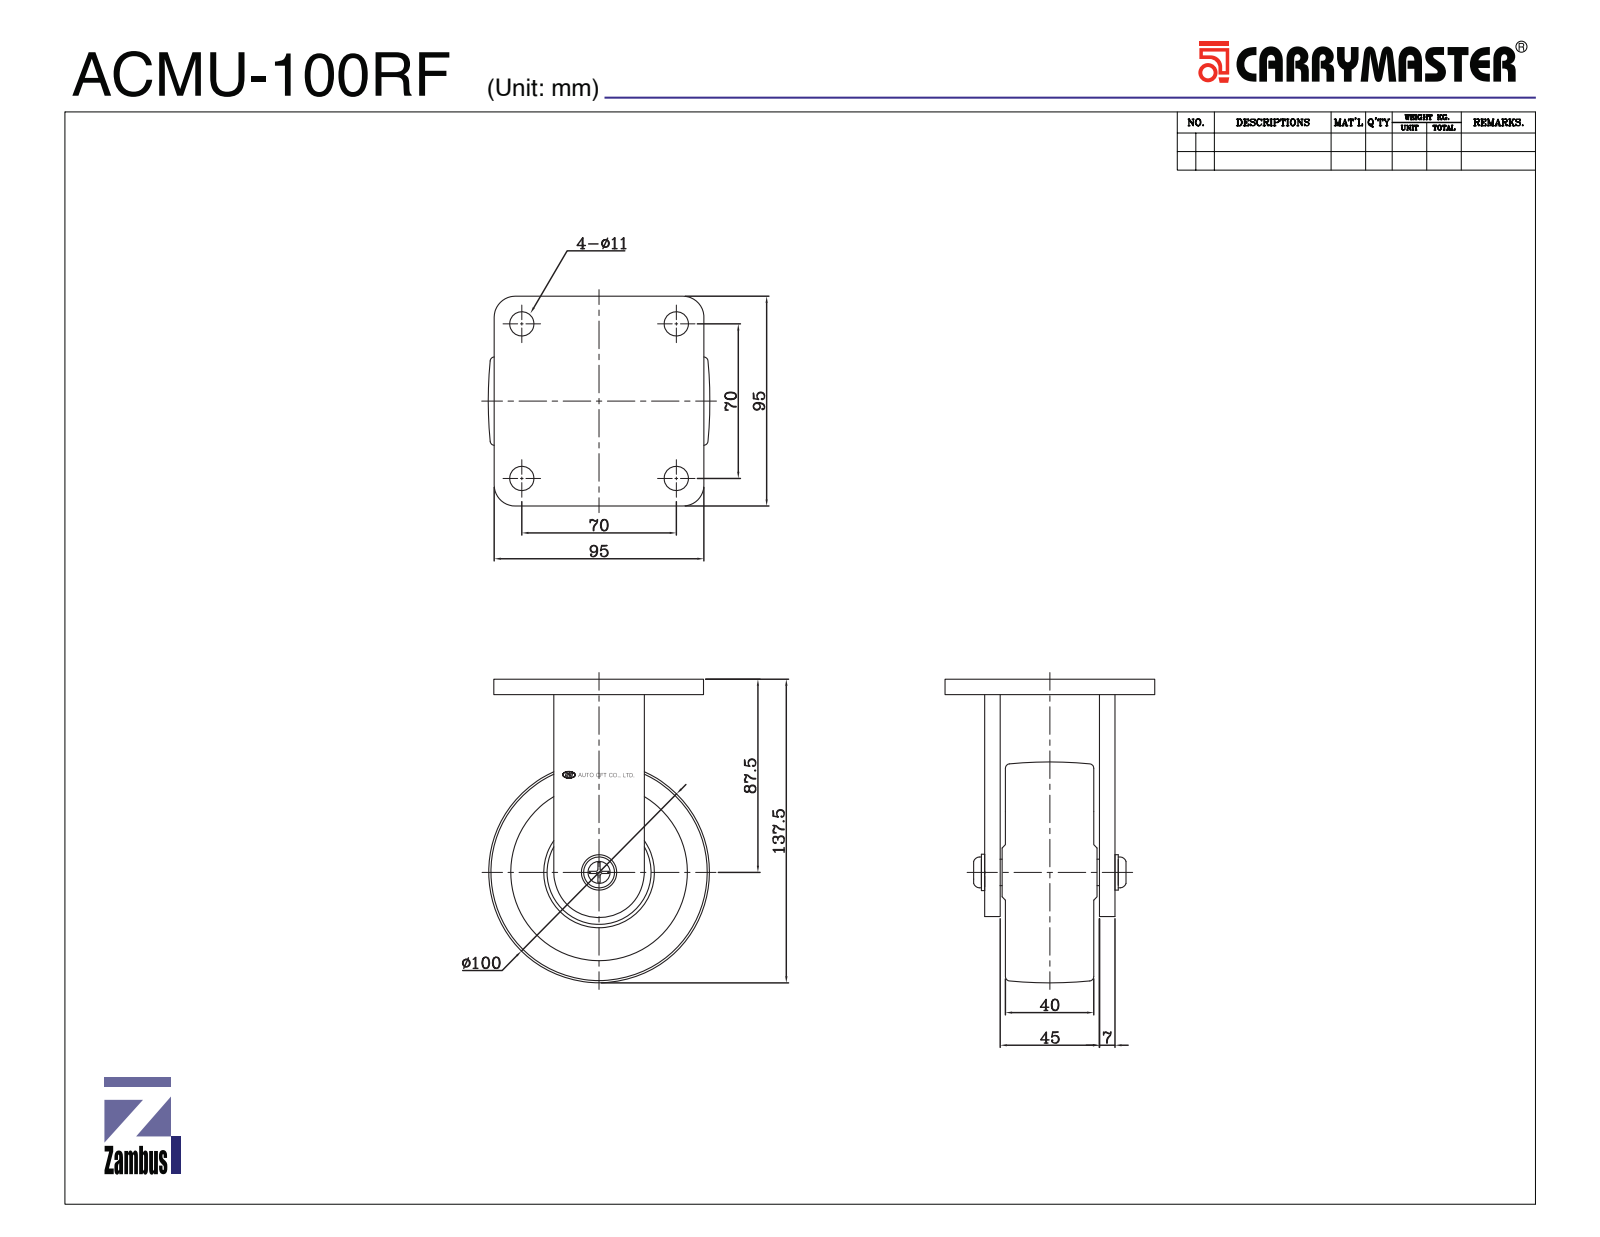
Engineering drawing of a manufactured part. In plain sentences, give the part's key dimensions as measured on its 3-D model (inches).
The part is named "ACMU-100RF". Its 3-D file was written by "SolidWorks 2015 (CONFIG_CONTROL_DESIGN)". It is 7 solids with 987 faces: 246 planar, 97 cylindrical and 644 other. Overall it measures 5.413 by 3.937 by 3.74 inches. Its volume is 22.74 cubic inches and its surface area 166.7 square inches. Round holes: 4 of diameter 0.433, 1 of diameter 0.268, 1 of diameter 0.484, 1 of diameter 1.39. Round bosses or shafts: 1 of diameter 3.937, 1 of diameter 0.63, 1 of diameter 0.551, 1 of diameter 0.472, 1 of diameter 0.315. Partial cylindrical surfaces (rounded edges, fillets, slot ends): 16 of radius 0.157, 10 of radius 0.039, 4 of radius 0.374, 2 of radius 0.02, 1 of radius 0.807. The main face-to-face distances are 0.276, 0.374, 1.949, 0.098, 2.047, 1.673, 1.575, 1.772, 2.323, 2.008. The hole center spacings are 2.756, 3.897.
